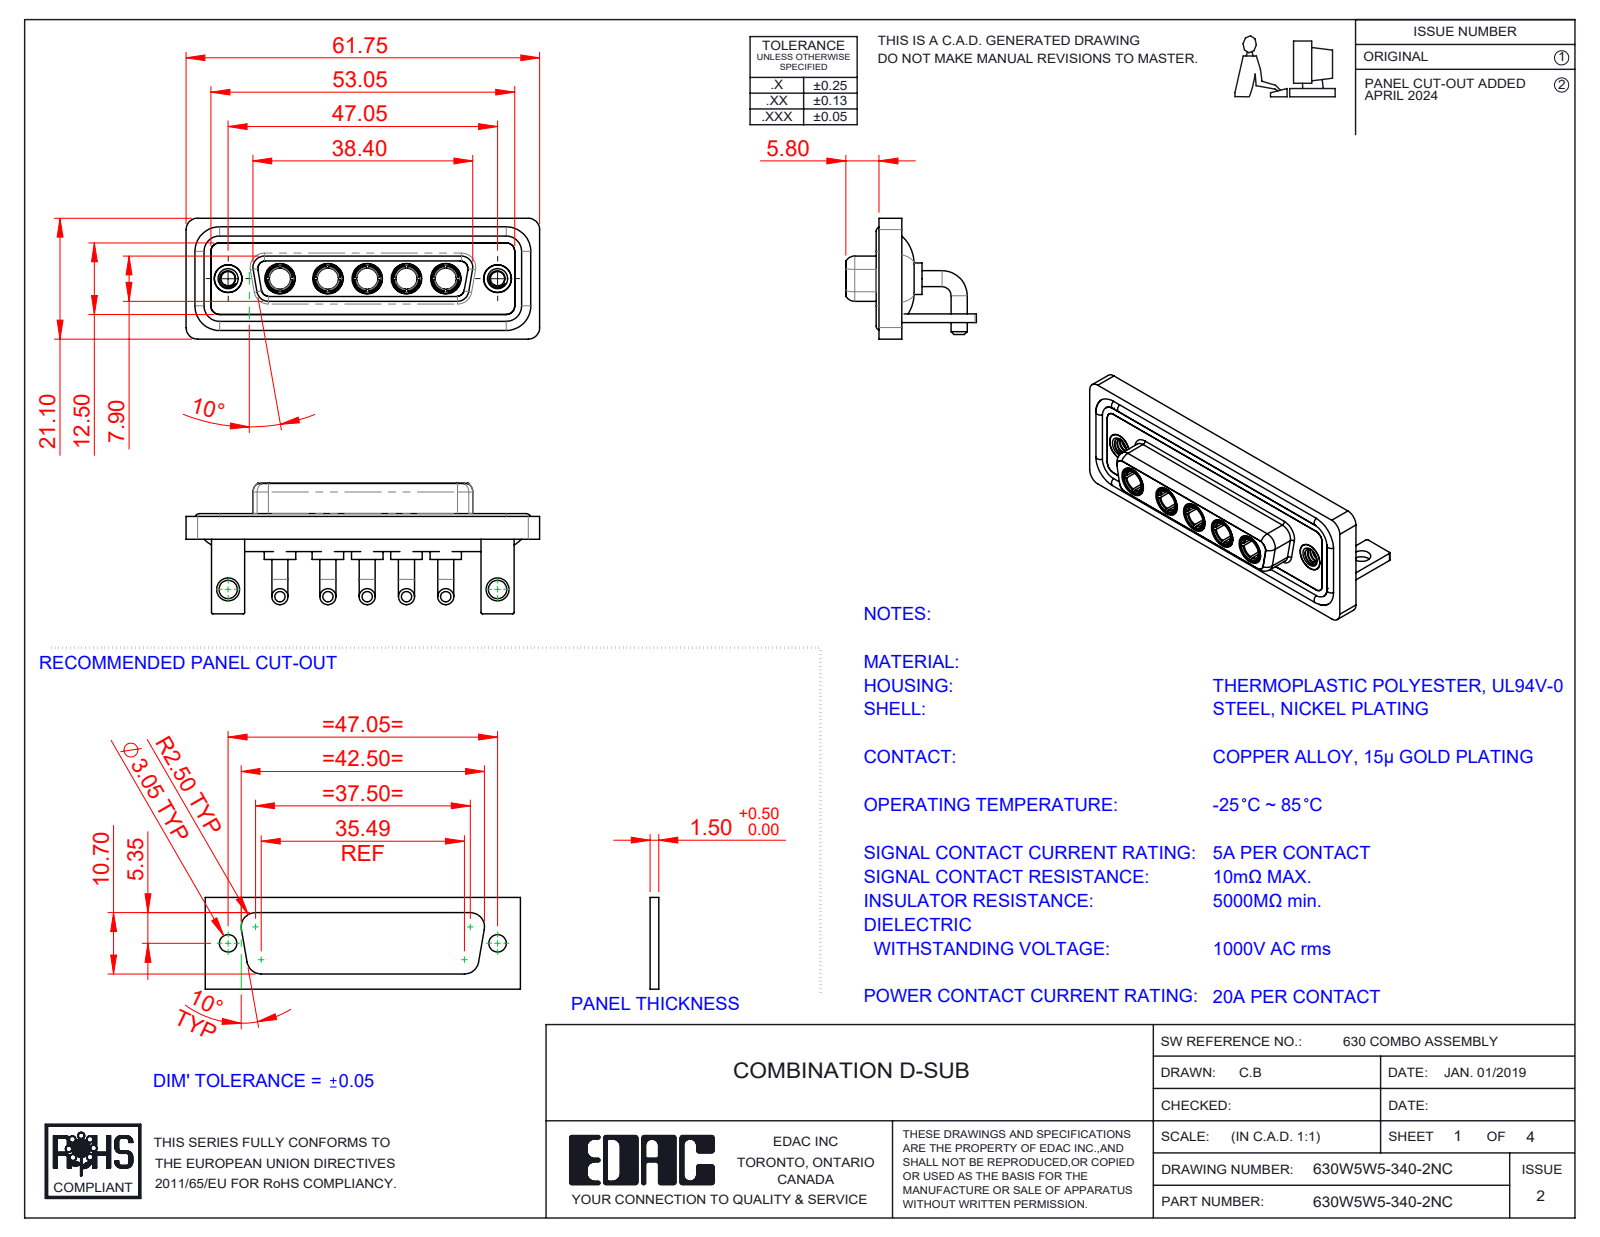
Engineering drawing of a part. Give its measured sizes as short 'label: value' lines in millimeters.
name: 630Combo Shell Front_25 Contacts; 630Combo Waterproof Housing_25 Contacts; Power Socket_20A RA; 630W5W5-340-2NC (+4 more)
written by: SolidWorks 2023 (CONFIG_CONTROL_DESIGN)
unit: mm
bodies: 19 solids, 818 faces (270 planar, 335 cylindrical, 213 other)
size: 61.75 × 22.8 × 21.1
volume: 8 794 mm³; area: 14 552 mm²
holes: 7× ⌀4.85, 5× ⌀3.7, 5× ⌀5.3, 2× ⌀2.5, 2× ⌀3.2, 2× ⌀4, 2× ⌀4.05, 2× ⌀5
bosses: 10× ⌀2.8, 5× ⌀5.5, 5× ⌀5.2, 5× ⌀4.96, 5× ⌀4.75, 5× ⌀3.75, 4× ⌀1.6, 2× ⌀4.95
rounds: 19× R2, 18× R1.5, 16× R0.25, 8× R1.35, 8× R1.6, 5× R0.5, 5× R2.1, 4× R0.6
face distances: 0.4, 1.8, 2.9, 3.7, 1.5, 4.1, 1.1, 1.4, 1.6, 2.5
hole spacings: 6.86, 9.04, 38.01, 47.05, 6.87, 8.38, 13.72, 13.73
